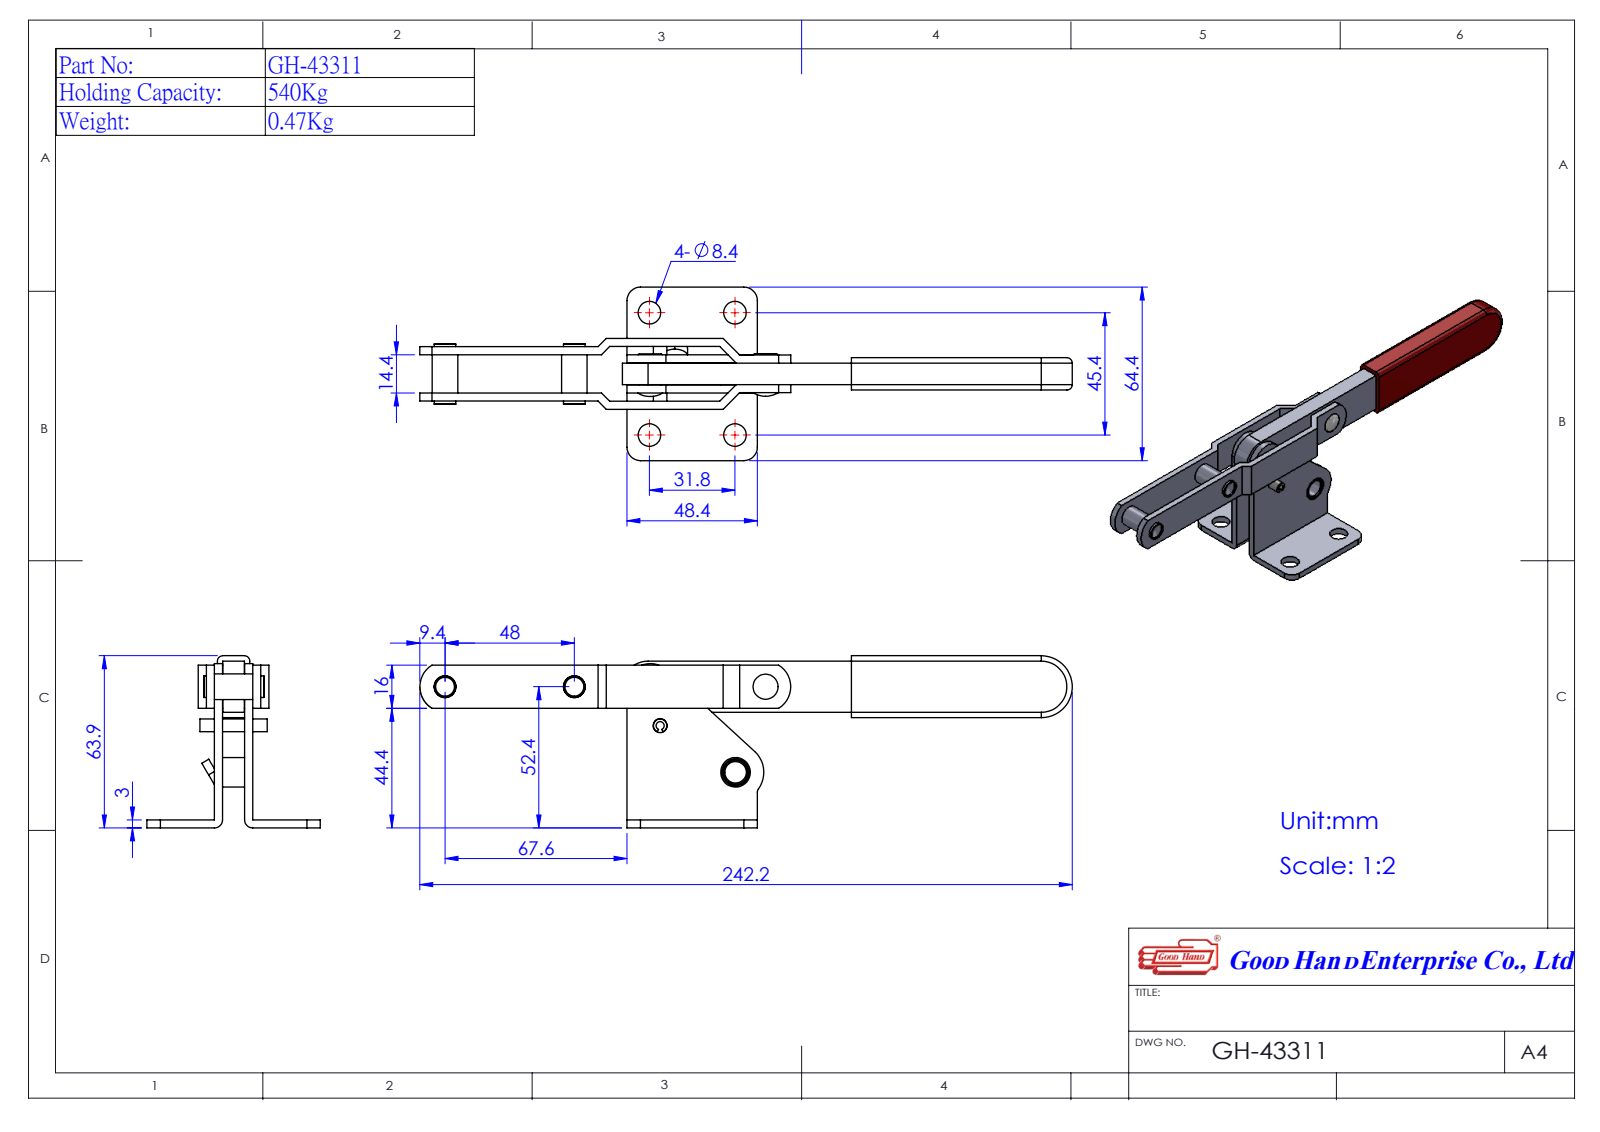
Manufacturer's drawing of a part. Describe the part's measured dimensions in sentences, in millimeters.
The part is named "GH-43311(簡化); Group3^GH-43311(簡化); 14331101-1^GH-43311(簡化); Group2^GH-43311(簡化)". Its 3-D file was written by "SolidWorks 2016 (AUTOMOTIVE_DESIGN)". It is 3 solids with 155 faces: 70 planar, 62 cylindrical and 23 other. Overall it measures 242.2 by 64.4 by 63.9 millimeters. Its volume is 70 840 cubic millimeters and its surface area 38 331 square millimeters. Round holes: 4 of diameter 8.5, 2 of diameter 6, 1 of diameter 3, 1 of diameter 11. Round bosses or shafts: 3 of diameter 8, 2 of diameter 9.5, 1 of diameter 5. Partial cylindrical surfaces (rounded edges, fillets, slot ends): 6 of radius 5, 2 of radius 9.35, 1 of radius 2, 1 of radius 8.6, 1 of radius 9.5, 1 of radius 10.5, 1 of radius 11.5. The main face-to-face distances are 3.1, 3, 11.2, 14.2, 14.3, 2, 11.1, 1.1, 13.1, 1.9. The hole center spacings are 31.75, 45.4, 55.4, 14.92, 32.91, 33.65, 41.73, 42.85.
